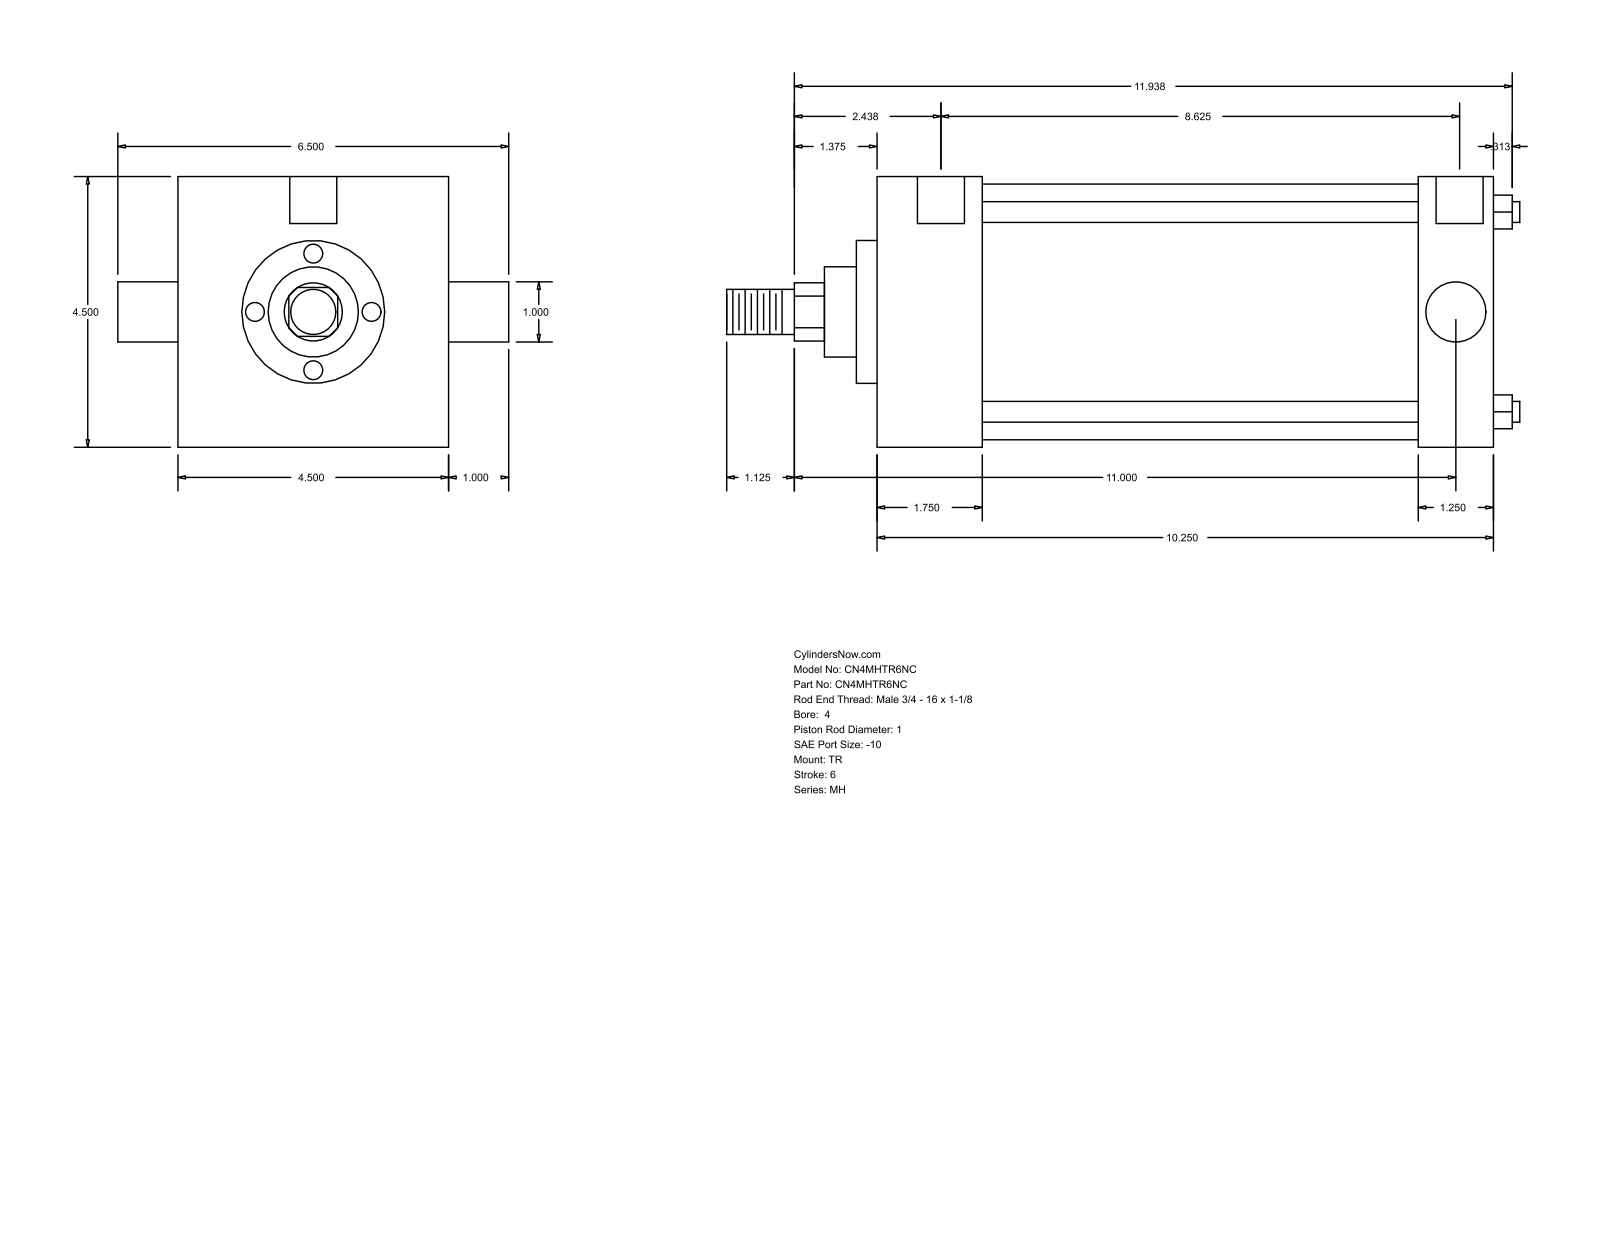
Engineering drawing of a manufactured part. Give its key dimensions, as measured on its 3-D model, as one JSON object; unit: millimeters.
{"part_name": "MH_TR__0400_1", "step_written_by": "GSSL Pune (CONFIG_CONTROL_DESIGN)", "units": "millimeters", "bodies": {"solids": 0, "faces": 86, "planar": 61, "cylindrical": 25, "other": 0}, "overall_size": [334.96, 165.1, 114.3], "round_holes": [[8.73, 3], [19.84, 2]], "round_bosses_or_shafts": [[8.76, 4], [25.4, 2], [107.95, 1], [60.33, 1], [38.1, 1], [19.05, 1]], "partial_cylinders_radius": [[12.29, 1]], "face_to_face_distances": [114.3, 260.35, 44.46, 215.89, 228.6, 184.14, 31.75, 8.73, 53.19, 237.33], "hole_center_spacings": [1.58, 220.66, 219.08, 222.24]}
